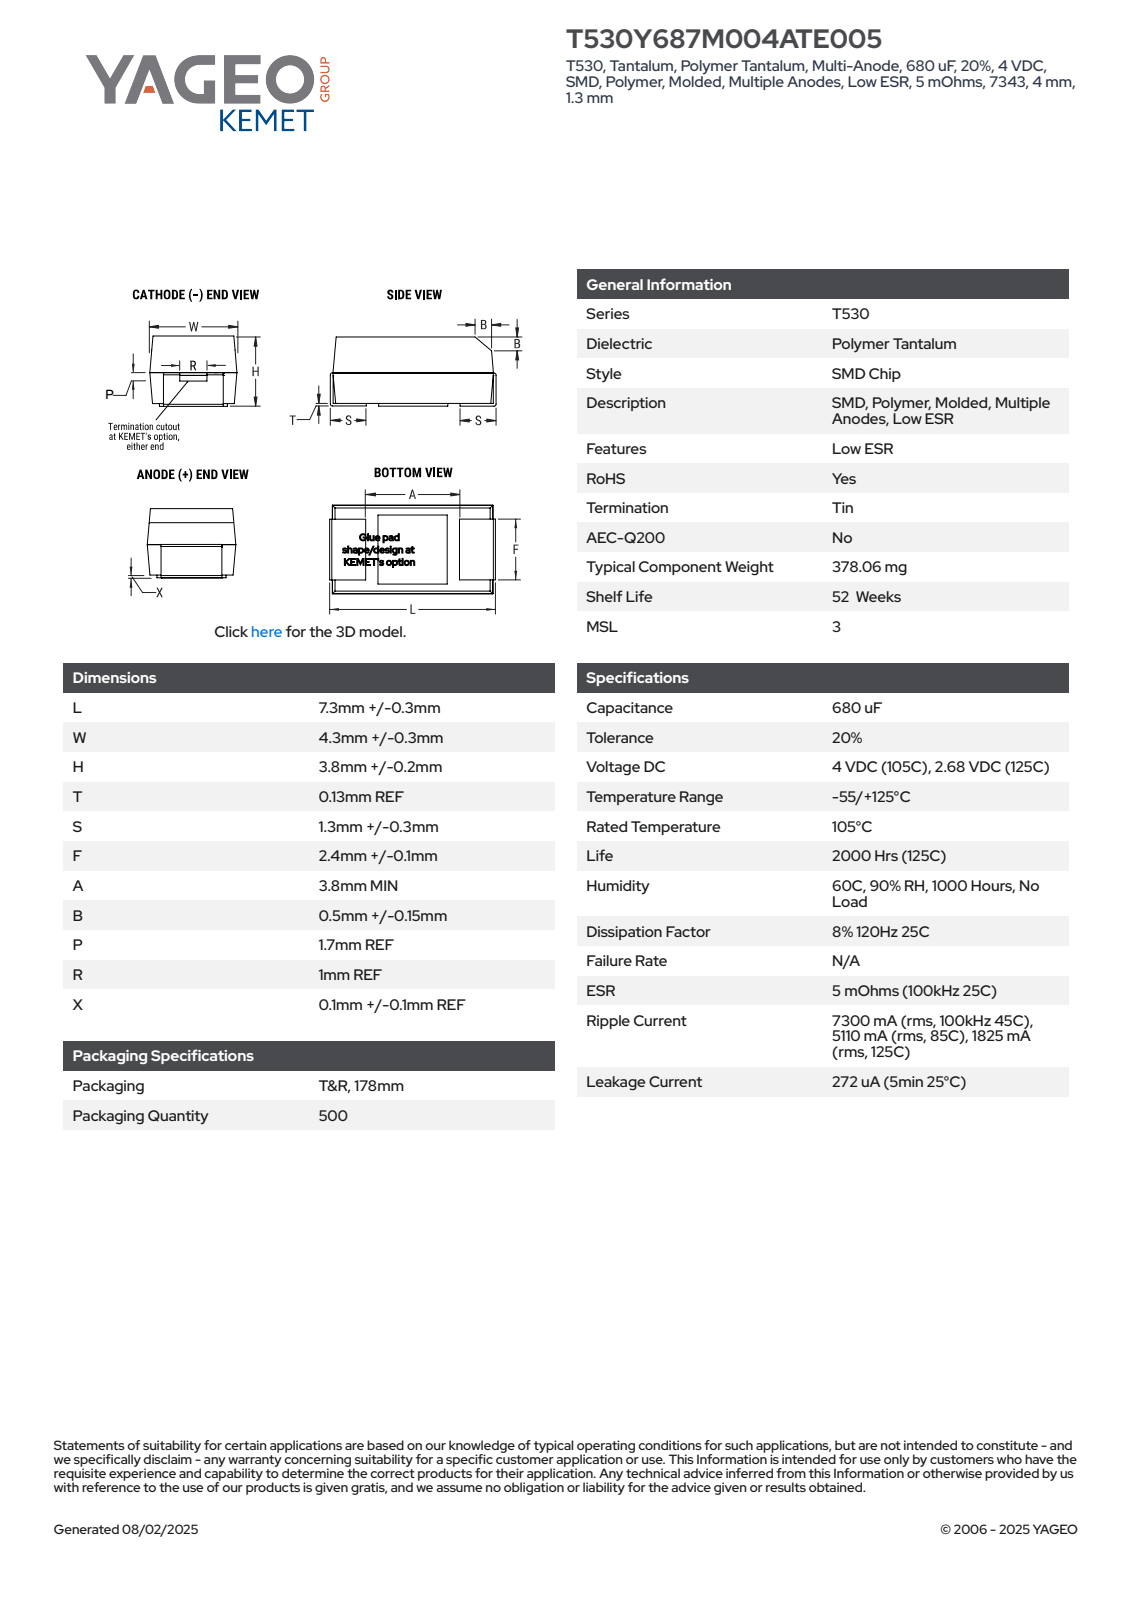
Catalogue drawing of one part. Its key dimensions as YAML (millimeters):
part_name: "CTSM_TCM2NKKO_7343_L7.6W4.6H4T0.13S1.3F2.5A3.8B0.65P1.7R1X0.1"
step_written_by: "SolidWorks 2021 (AUTOMOTIVE_DESIGN)"
units: millimeters
bodies: {solids: 4, faces: 100, planar: 95, cylindrical: 5, other: 0}
overall_size: [7.6, 4.6, 4.04]
volume: 122
surface_area: 169
partial_cylinders:
  - {radius: 0.1, count: 4}
face_to_face_distances: [4.56, 3.9, 4, 7.47, 4.03, 7.6, 7.34, 2.5, 2.4, 5.2]
